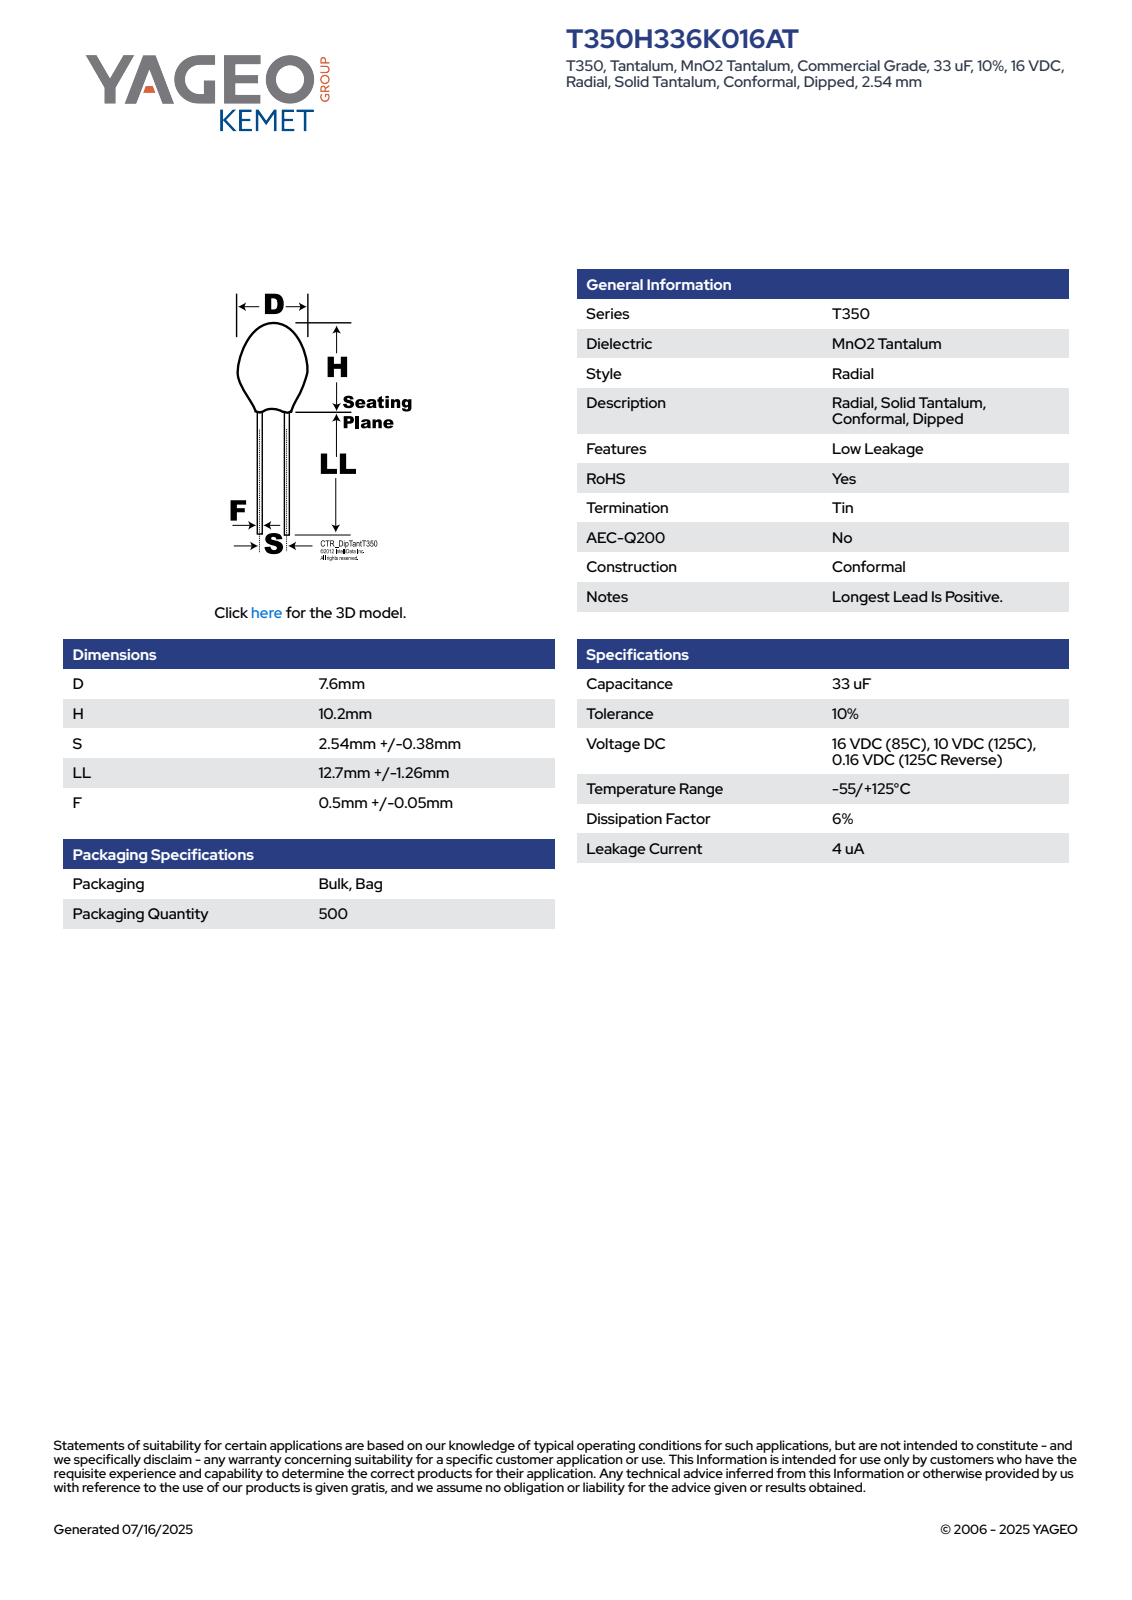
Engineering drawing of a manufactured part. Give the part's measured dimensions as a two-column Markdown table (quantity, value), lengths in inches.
| quantity | value |
| --- | --- |
| part name | CTR_T350_D7.6H10.2S2.54LL13.96F0.55 |
| STEP written by | SolidWorks 2014 (AUTOMOTIVE_DESIGN) |
| units | inches |
| bodies | 1 solid, 72 faces (26 planar, 9 cylindrical, 37 other) |
| overall size | 0.951 × 0.299 × 0.299 |
| volume | 0.024 in³ |
| surface area | 0.488 in² |
| round bosses / shafts (diameter × count) | 0.022 × 2, 0.299 × 1 |
| partial cylindrical surfaces (radius × count) | 0.149 × 1 |
| main face-to-face distances | 0.402, 0.55, 0.951, 0.774, 0.225, 0.177, 0.731, 0.181, 0.044, 0.22 |
